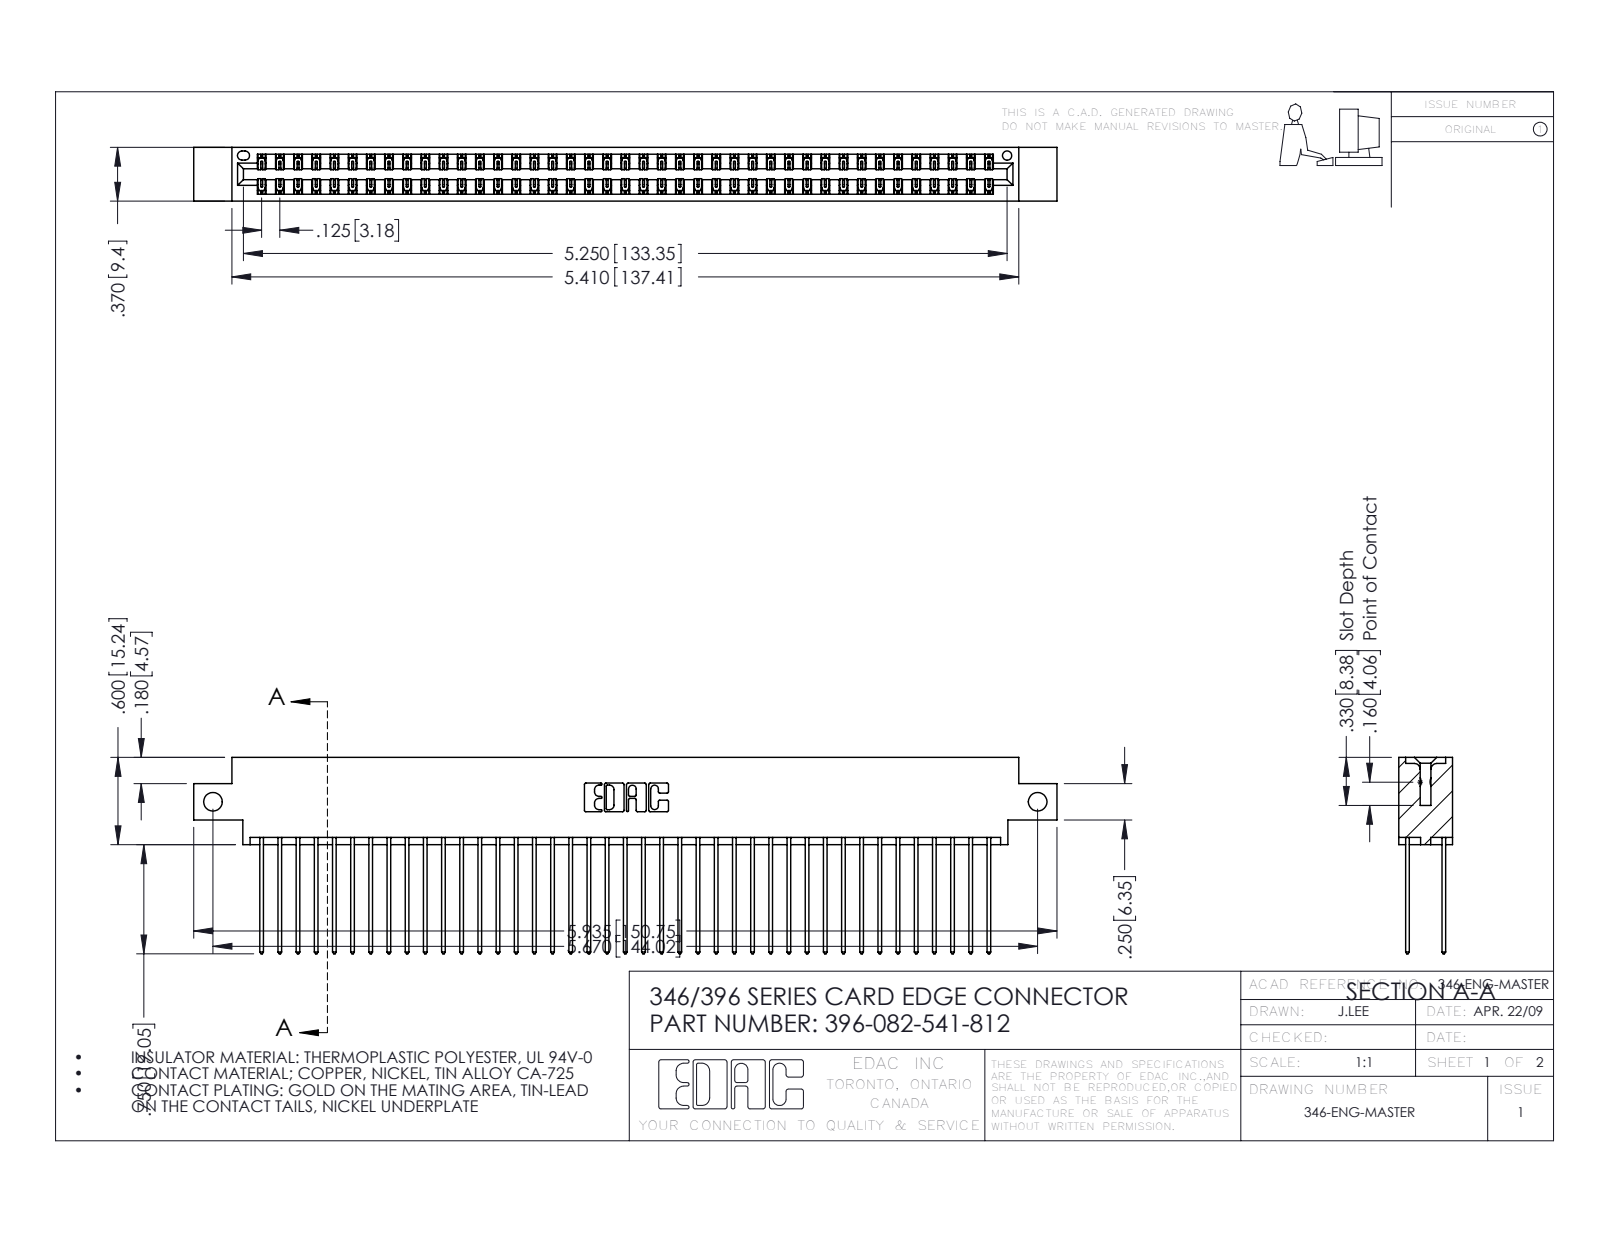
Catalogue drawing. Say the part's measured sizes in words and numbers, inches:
The part is named "345-292-001_345-293-141; 346 Part_0.170 Offset - Side Mount; 396-082-541-812". Its 3-D file was written by "SolidWorks 2016 (CONFIG_CONTROL_DESIGN)". It is 83 solids with 4390 faces: 2950 planar, 1440 cylindrical and 0 other. Overall it measures 5.935 by 1.35 by 0.37 inches. Its volume is 0.911 cubic inches and its surface area 35.33 square inches. Round holes: 2 of diameter 0.128, 1 of diameter 0.064. Partial cylindrical surfaces (rounded edges, fillets, slot ends): 123 of radius 0.006, 82 of radius 0.01, 22 of radius 0.01, 6 of radius 0.007, 6 of radius 0.031, 3 of radius 0.026, 2 of radius 0.014, 2 of radius 0.022. The main face-to-face distances are 0.048, 0.322, 0.25, 0.072, 0.298, 0.025, 0.37, 0.275, 0.225, 0.148. The hole center spacings are 5.67.
